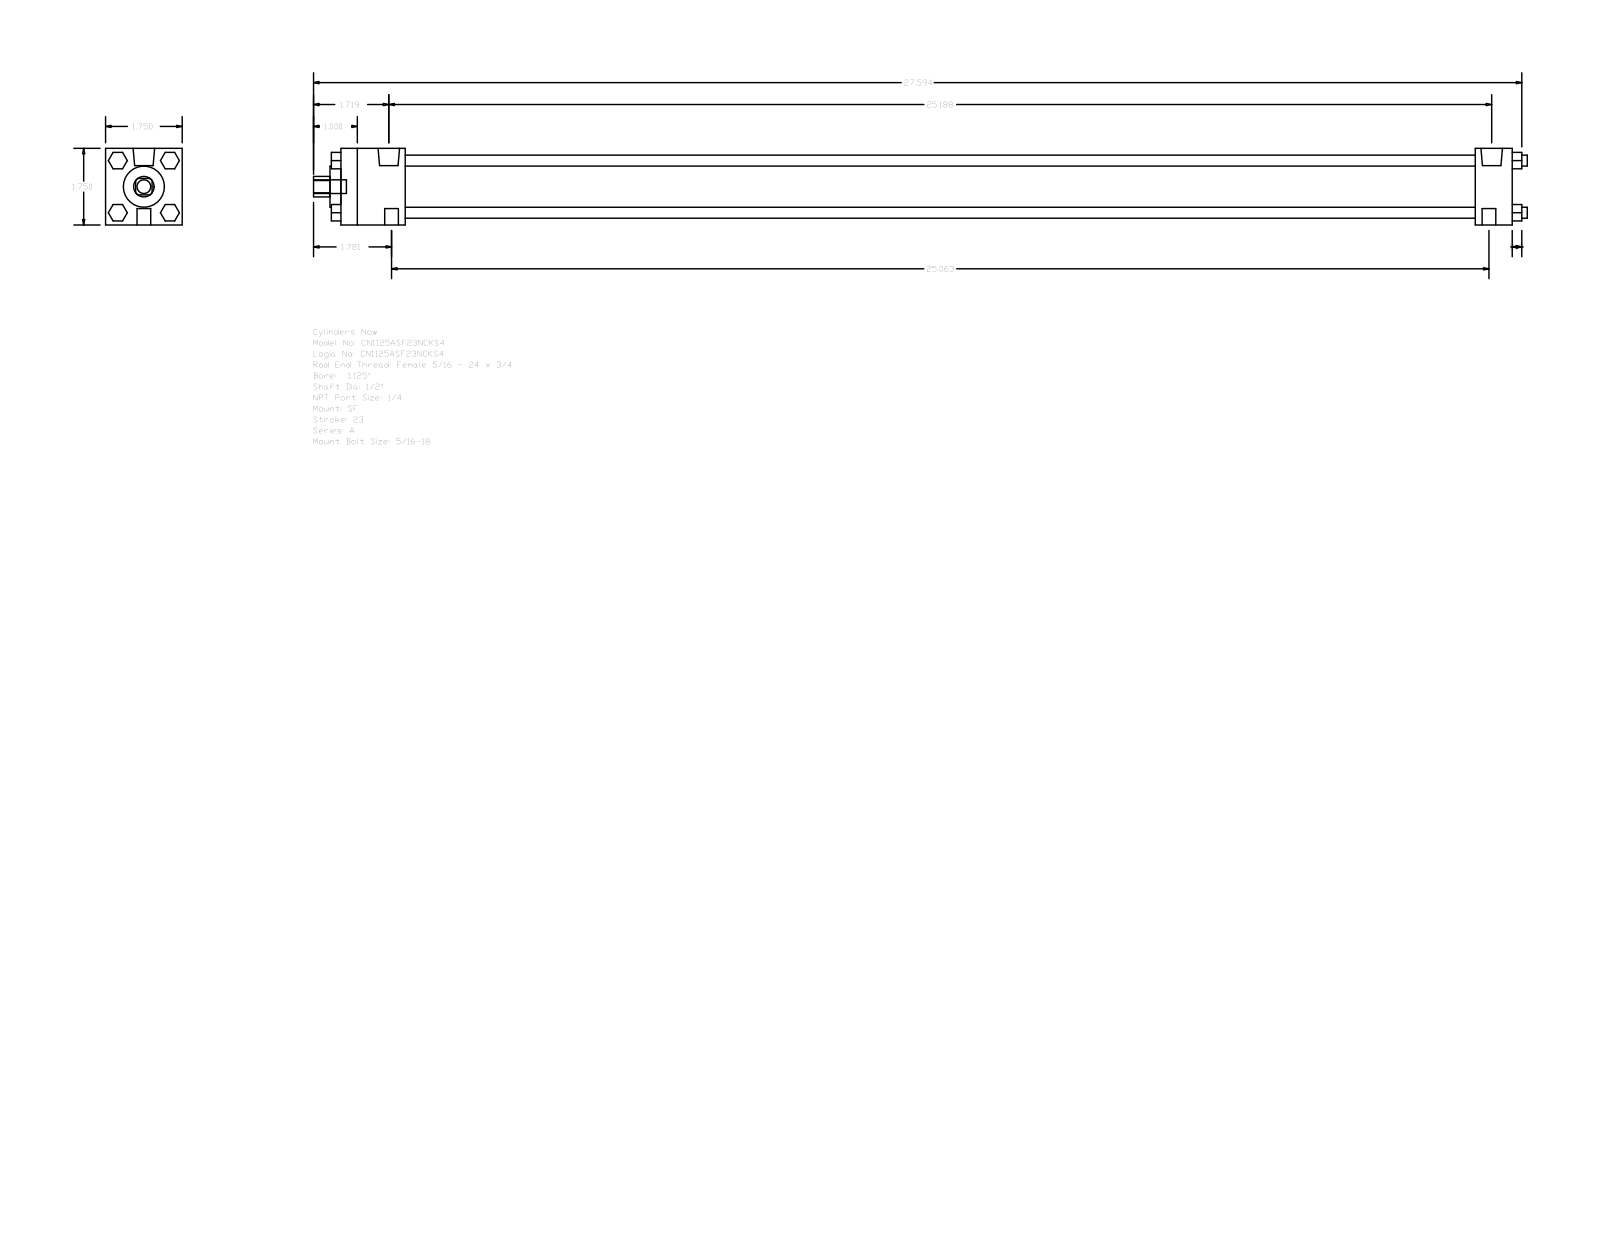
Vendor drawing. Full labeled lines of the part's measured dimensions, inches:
Part name (STEP PRODUCT): A_SF__0112_0.5
STEP written by: GSSL Pune (CONFIG_CONTROL_DESIGN)
Units: inches
Bodies: 0 solids, 120 faces (92 planar, 28 cylindrical, 0 other)
Overall size (bounding box): 27.719 × 1.75 × 1.75
Round holes (diameter × count): ⌀0.5 ×1, ⌀0.937 ×1, ⌀1.255 ×1
Round bosses / shafts (diameter × count): ⌀0.25 ×4, ⌀0.313 ×3, ⌀0.492 ×2, ⌀0.219 ×2
Partial cylindrical surfaces — rounded edges, fillets, slot ends (radius × count): R0.234 ×1
Main face-to-face distances: 1.75, 26.75, 25.906, 0.844, 1.469, 24.437, 25.281, 0.375, 0.22, 0.375
